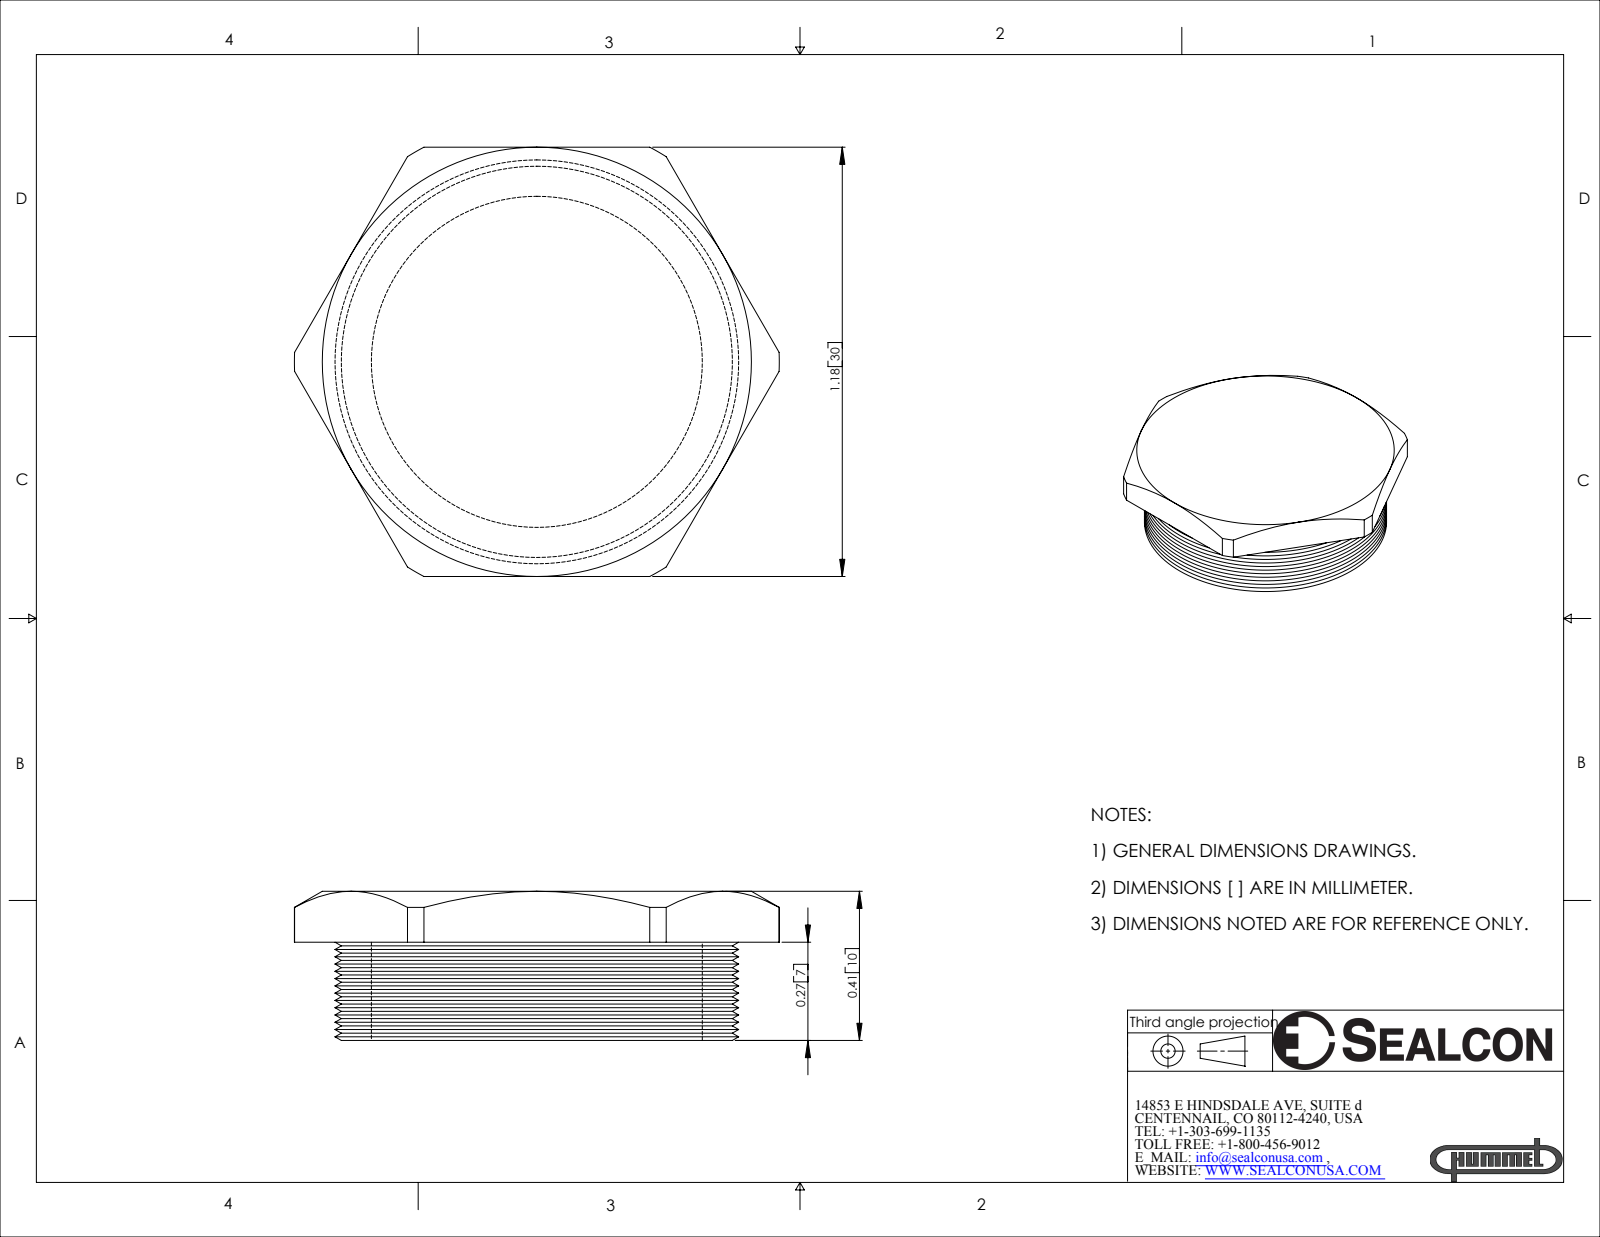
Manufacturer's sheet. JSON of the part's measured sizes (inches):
{"part_name": "HP-21-BR", "step_written_by": "SolidWorks 2007 (CONFIG_CONTROL_DESIGN)", "units": "inches", "bodies": {"solids": 1, "faces": 78, "planar": 10, "cylindrical": 8, "other": 60}, "overall_size": [1.333, 1.18, 0.41], "volume_in3": 0.244, "surface_area_in2": 5.486, "round_holes": [[0.91, 1]], "partial_cylinders_radius": [[0.667, 1]], "face_to_face_distances": [0.14, 0.27, 0.41, 1.18]}
